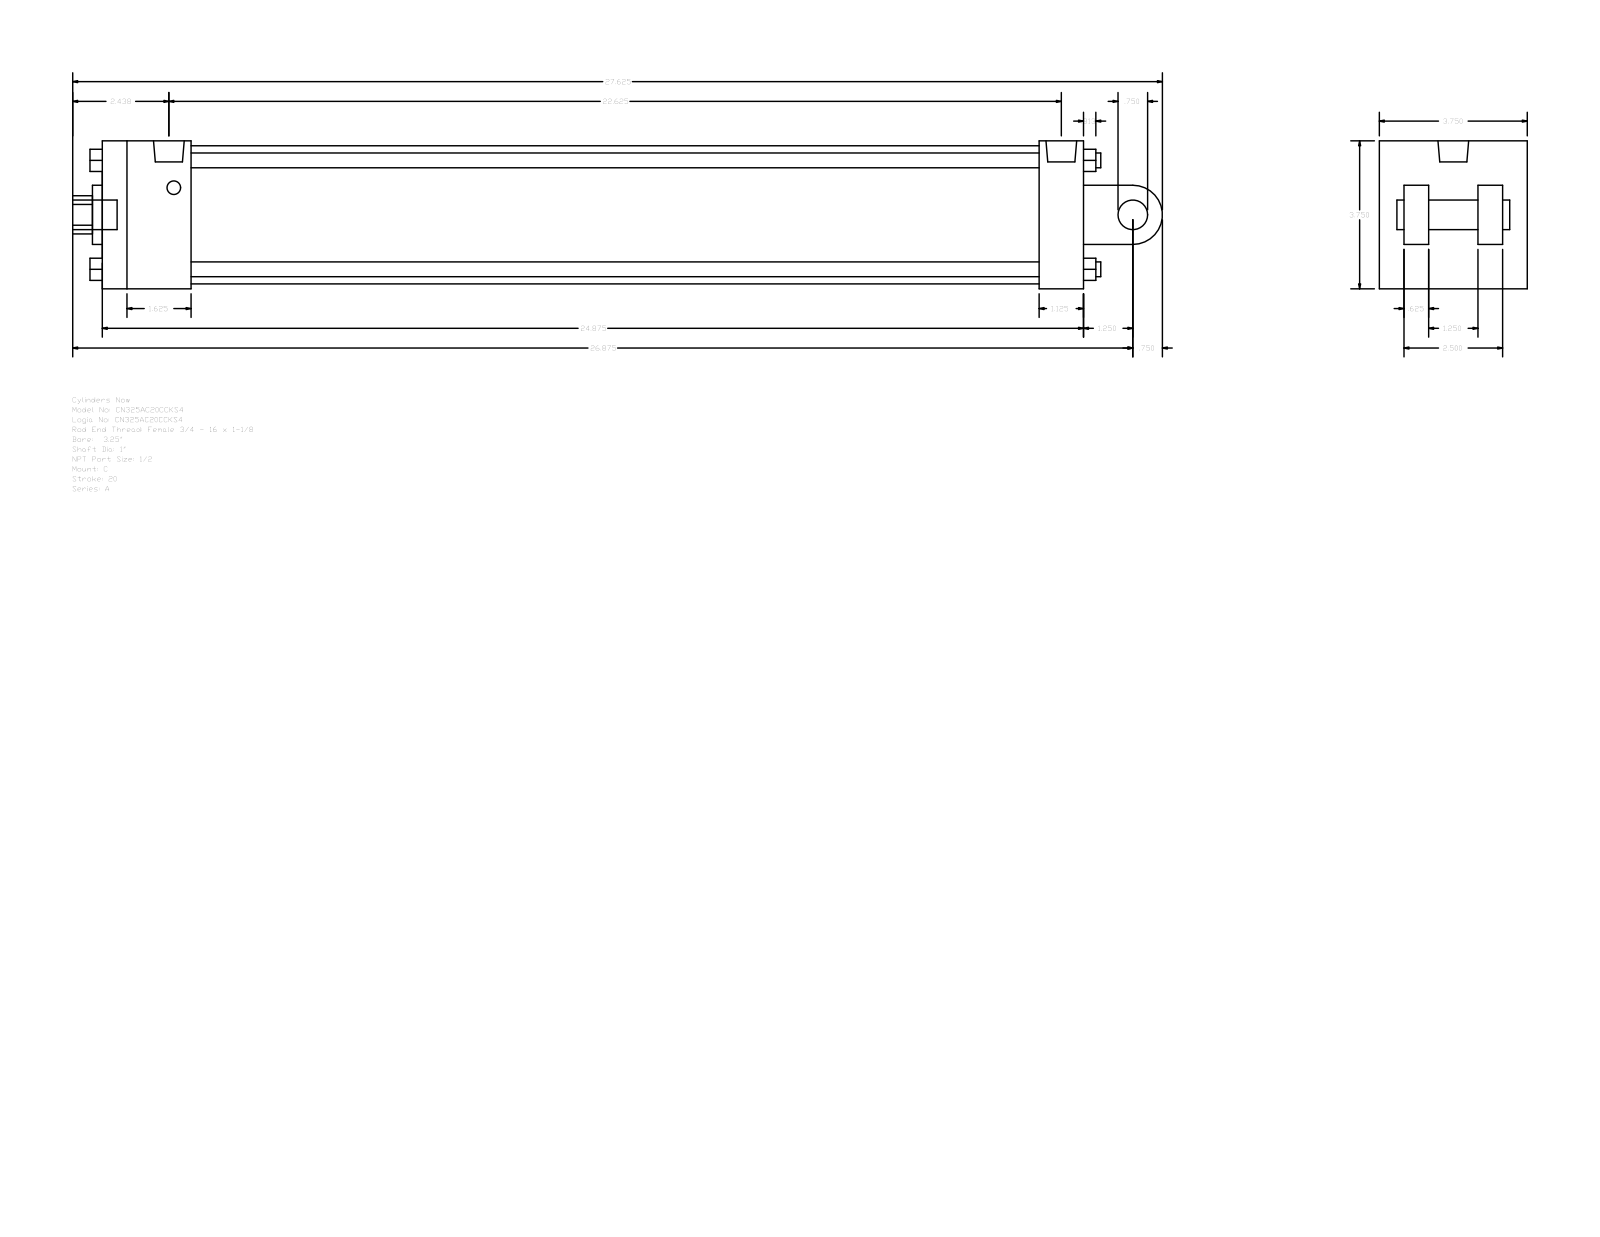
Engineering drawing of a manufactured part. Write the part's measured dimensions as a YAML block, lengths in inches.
part_name: "A_C__0325_1"
step_written_by: "GSSL Pune (CONFIG_CONTROL_DESIGN)"
units: inches
bodies: {solids: 0, faces: 135, planar: 102, cylindrical: 33, other: 0}
overall_size: [27.625, 3.75, 3.75]
round_holes:
  - {diameter: 0.344, count: 2}
  - {diameter: 0.778, count: 1}
  - {diameter: 1, count: 1}
  - {diameter: 1.5, count: 1}
  - {diameter: 3.5, count: 1}
round_bosses_or_shafts:
  - {diameter: 0.375, count: 4}
  - {diameter: 0.75, count: 2}
  - {diameter: 0.344, count: 2}
  - {diameter: 0.778, count: 1}
partial_cylinders:
  - {radius: 0.484, count: 1}
  - {radius: 0.75, count: 1}
face_to_face_distances: [3.75, 24.875, 0.625, 2.5, 1.875, 1.25, 3.125, 2.625, 23.75, 1.125]
hole_center_spacings: [0.125]
